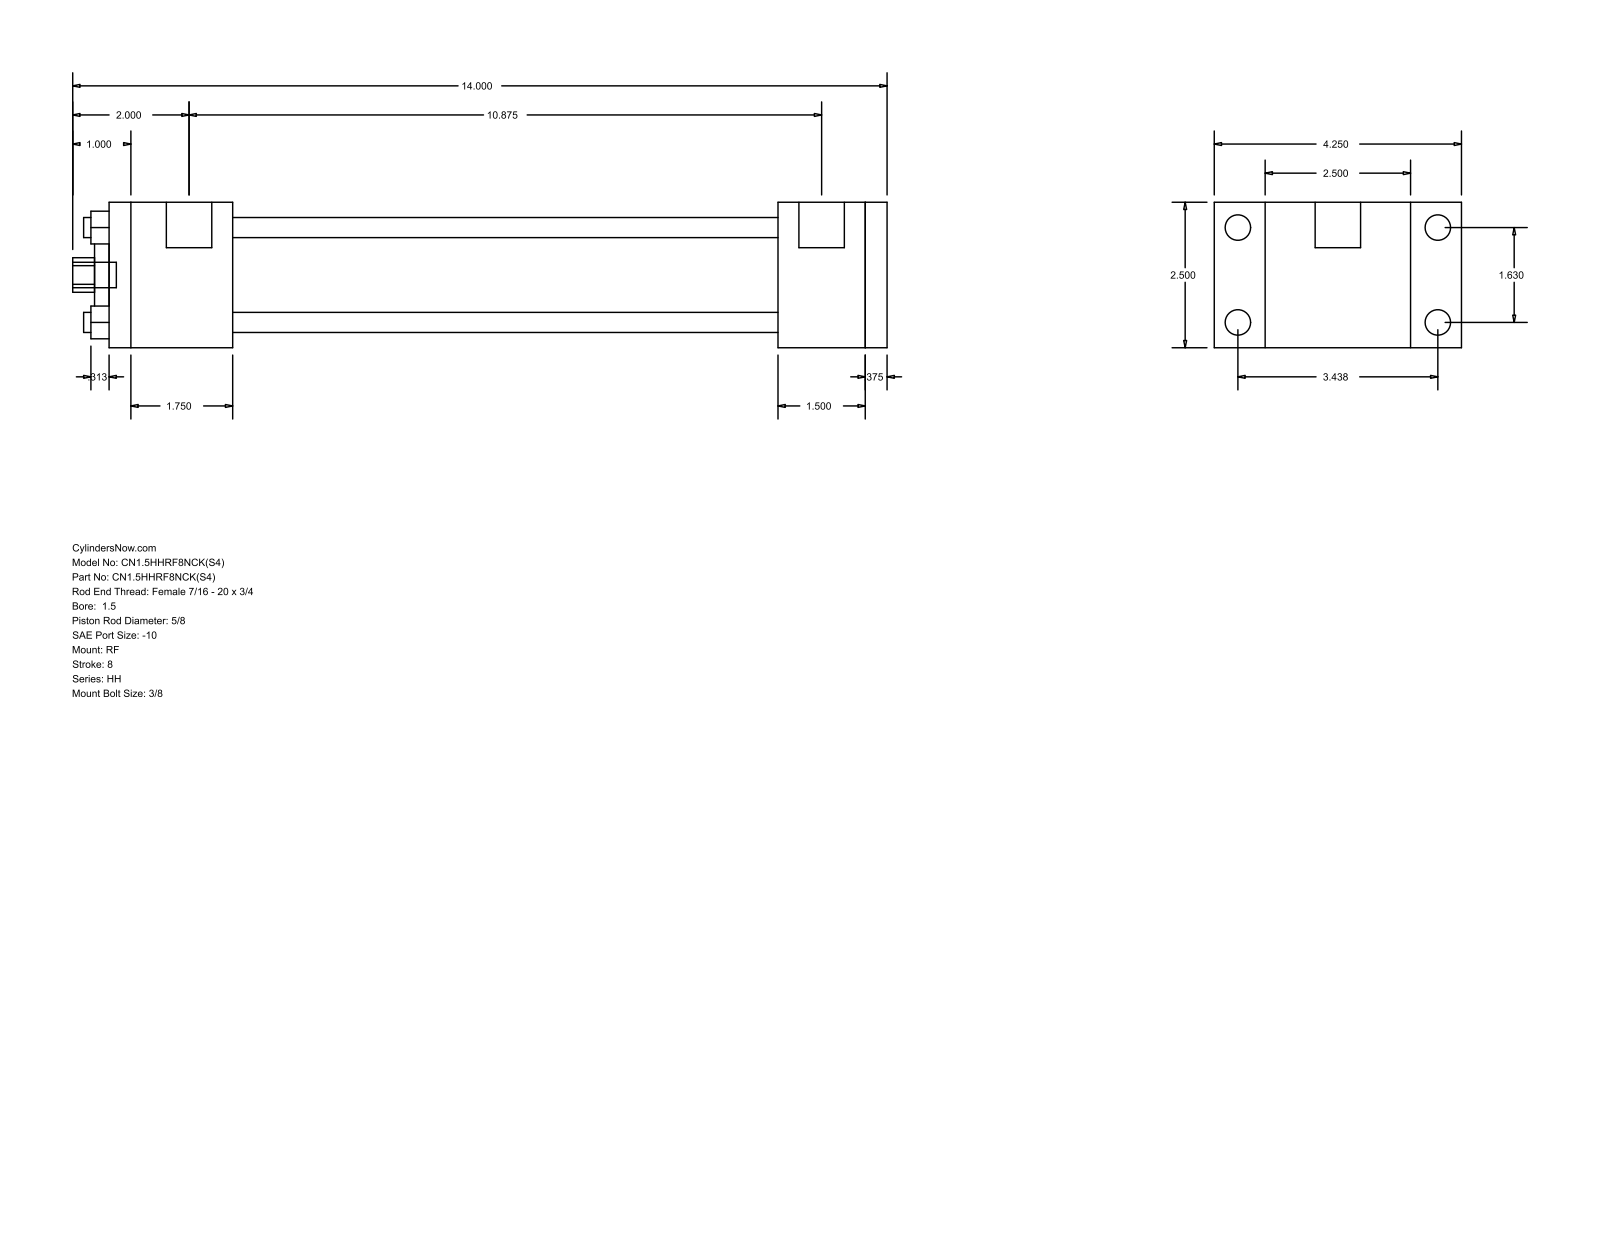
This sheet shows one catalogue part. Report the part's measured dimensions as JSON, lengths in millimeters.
{"part_name": "HH_RF__0150_0.625", "step_written_by": "GSSL Pune (CONFIG_CONTROL_DESIGN)", "units": "millimeters", "bodies": {"solids": 0, "faces": 92, "planar": 64, "cylindrical": 28, "other": 0}, "overall_size": [355.6, 107.95, 63.5], "round_holes": [[8.76, 4], [15.88, 1], [28.57, 1], [44.45, 1]], "round_bosses_or_shafts": [[11.13, 4], [5.56, 4], [19.84, 2], [11.11, 1]], "partial_cylinders_radius": [[7.54, 1]], "face_to_face_distances": [63.5, 339.72, 9.53, 330.19, 53.97, 292.1, 238.13, 276.22, 285.75, 38.09], "hole_center_spacings": [29.27, 41.4, 58.55]}
